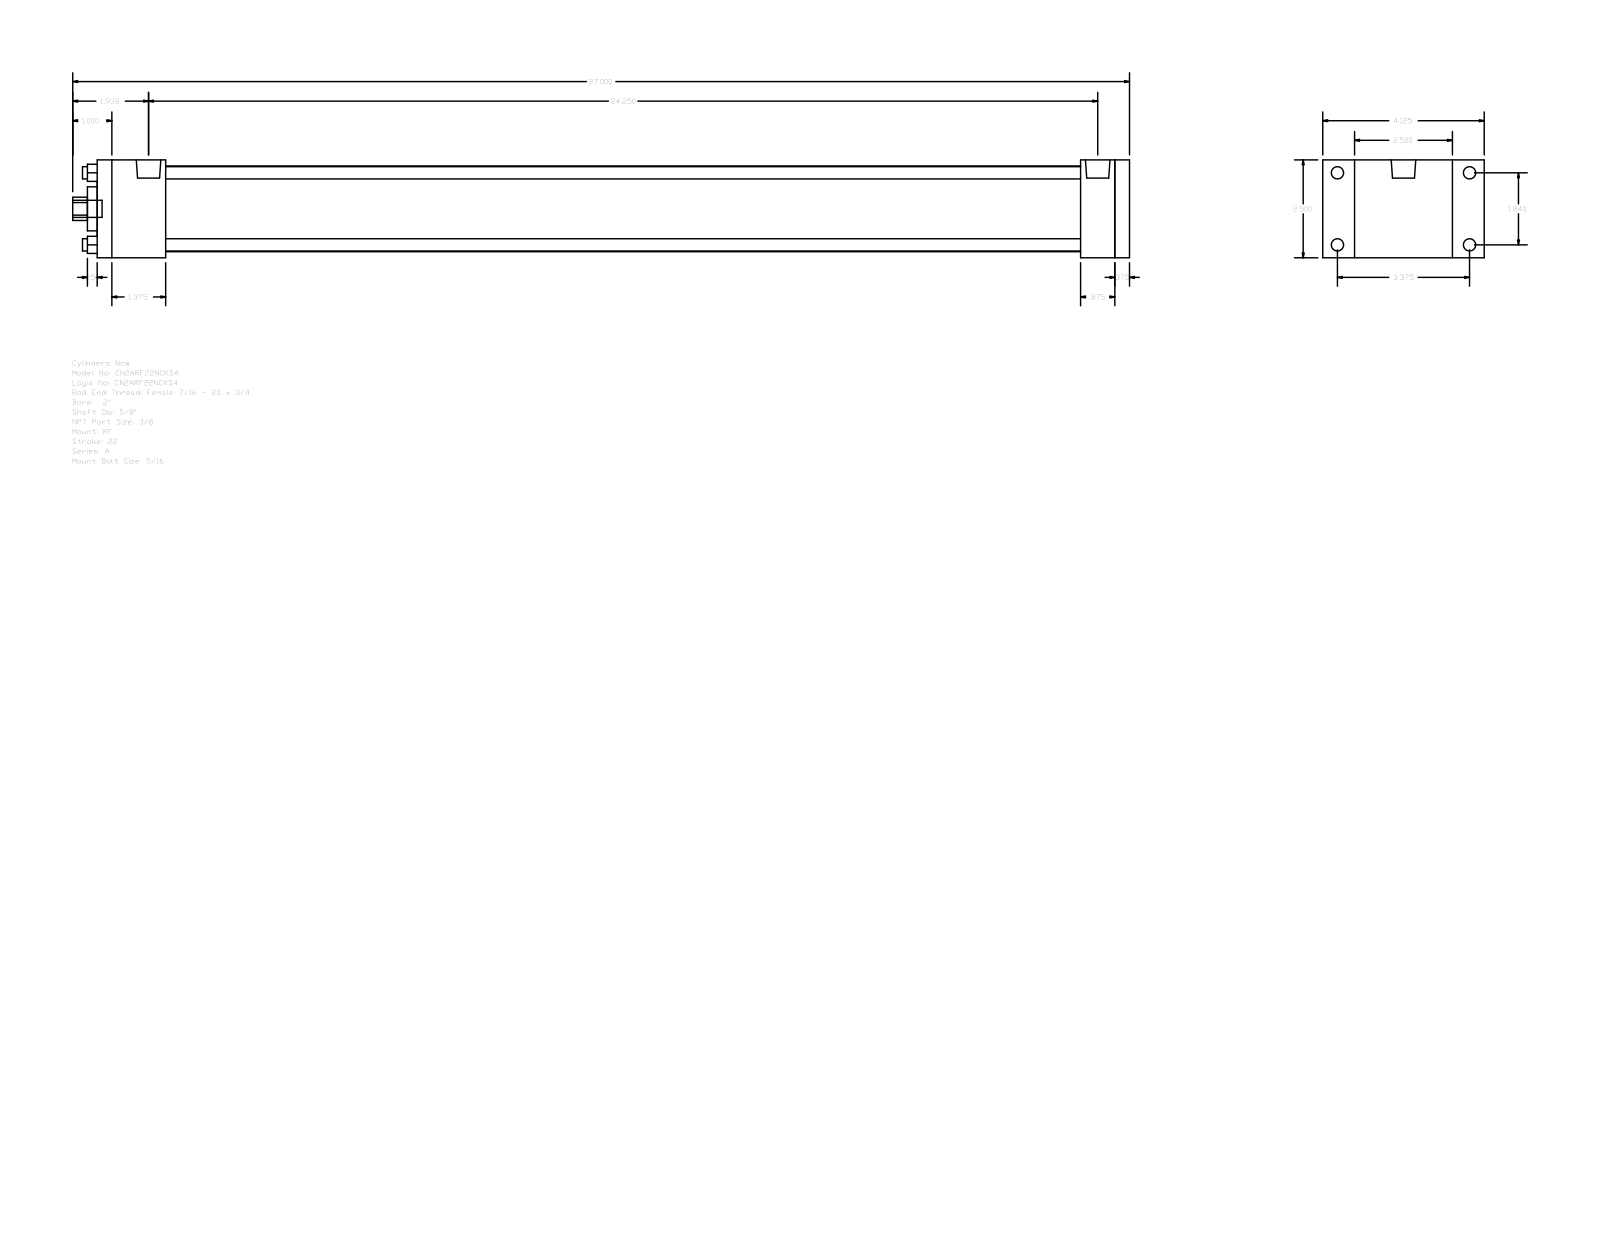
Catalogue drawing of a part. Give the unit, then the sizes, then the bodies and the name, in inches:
Units: inches
Overall size (bounding box): 27 × 4.125 × 2.5
Round holes (diameter × count): ⌀0.313 ×4, ⌀0.625 ×1, ⌀1.125 ×1, ⌀2.19 ×1
Round bosses / shafts (diameter × count): ⌀0.313 ×4, ⌀0.219 ×4, ⌀0.627 ×2, ⌀0.437 ×1
Partial cylindrical surfaces — rounded edges, fillets, slot ends (radius × count): R0.297 ×1
Main face-to-face distances: 2.5, 26.375, 0.375, 26, 1.75, 24.25, 24.625, 25.125, 23.375, 0.875
Hole centre spacings: 1.301, 1.84, 2.602
Bodies: 0 solids, 92 faces (64 planar, 28 cylindrical, 0 other)
Part name (STEP PRODUCT): A_RF__0200_0.625
STEP written by: GSSL Pune (CONFIG_CONTROL_DESIGN)
